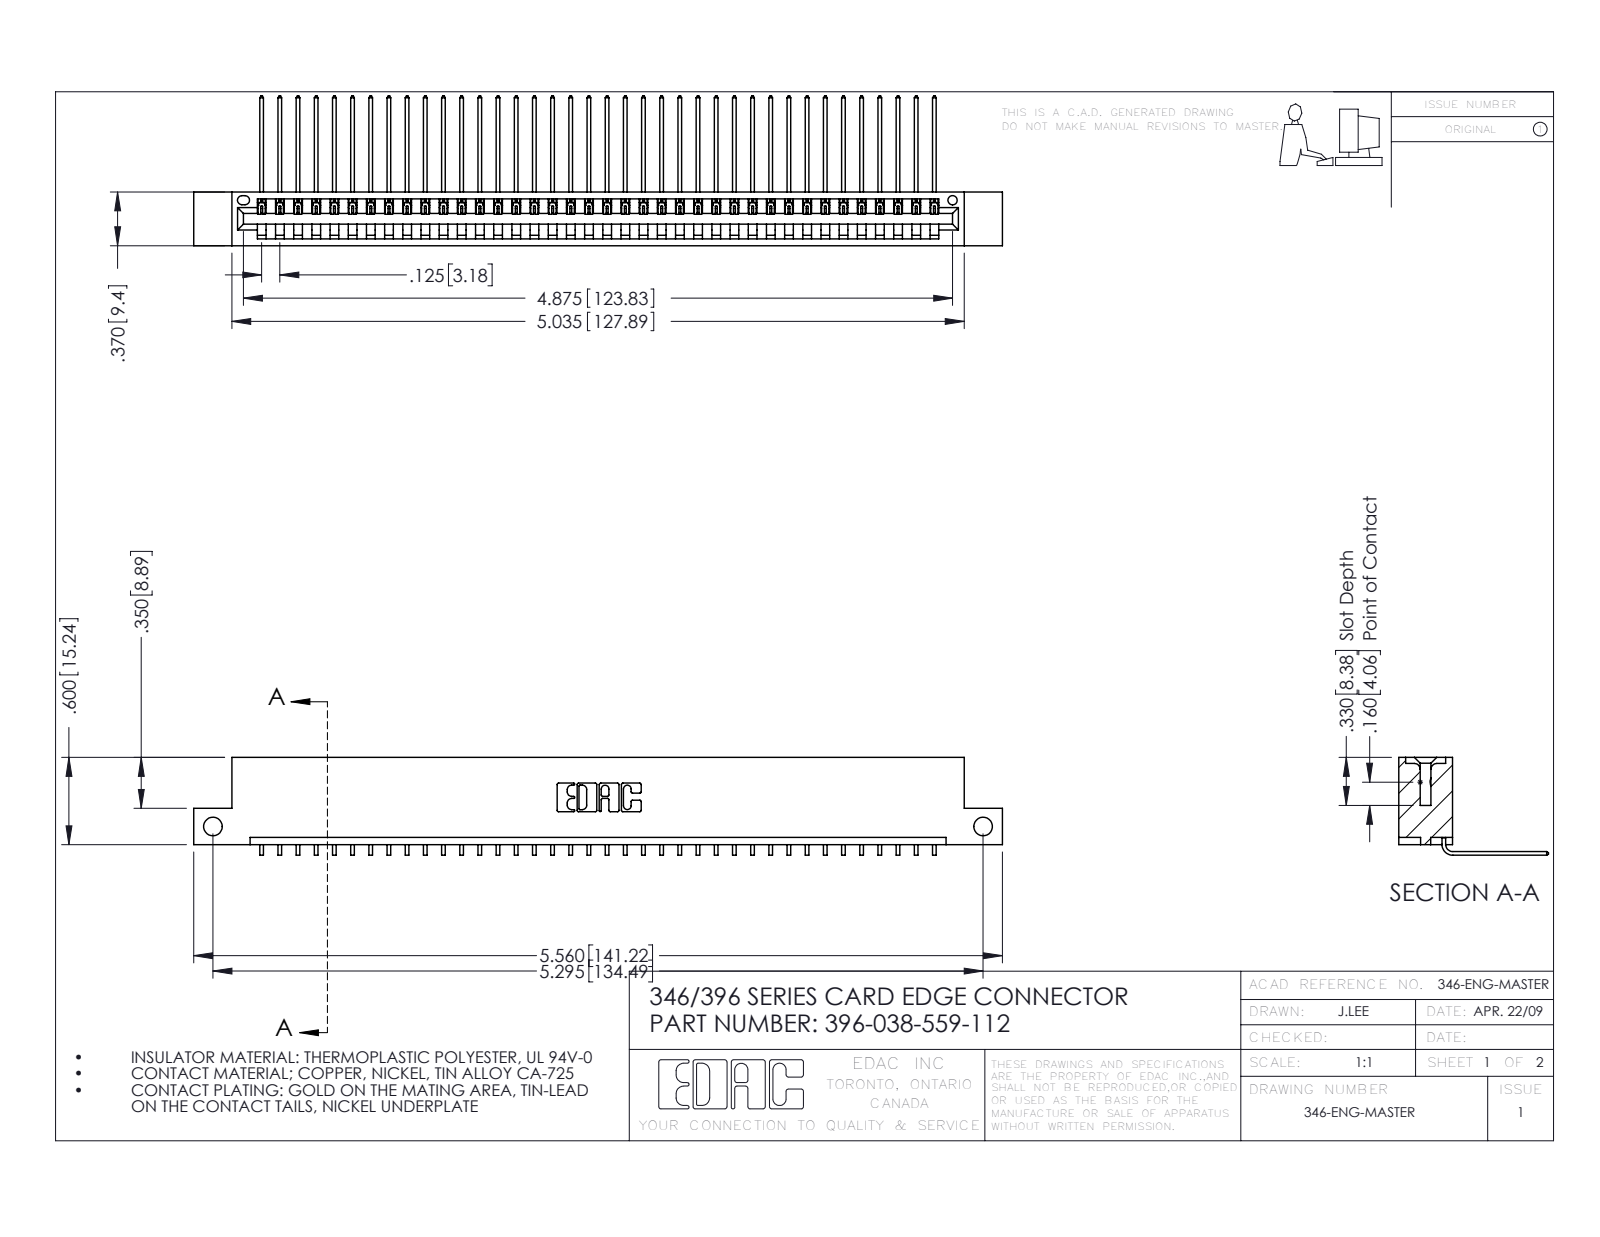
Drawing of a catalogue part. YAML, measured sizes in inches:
part_name: "345-292-001_558 559 Tail - 1; 346 Part_Flush Mounting Lugs - Side Mount; 396-038-559-112"
step_written_by: "SolidWorks 2016 (CONFIG_CONTROL_DESIGN)"
units: inches
bodies: {solids: 39, faces: 2402, planar: 1672, cylindrical: 730, other: 0}
overall_size: [5.56, 1.03, 0.673]
volume: 0.826
surface_area: 27.09
round_holes:
  - {diameter: 0.128, count: 2}
  - {diameter: 0.064, count: 1}
partial_cylinders:
  - {radius: 0.006, count: 76}
  - {radius: 0.01, count: 22}
  - {radius: 0.007, count: 6}
  - {radius: 0.031, count: 6}
  - {radius: 0.026, count: 3}
  - {radius: 0.031, count: 2}
  - {radius: 0.04, count: 2}
  - {radius: 0.014, count: 1}
face_to_face_distances: [0.048, 0.322, 0.37, 0.25, 0.072, 0.025, 0.298, 0.148, 0.222, 0.1]
hole_center_spacings: [5.295]
